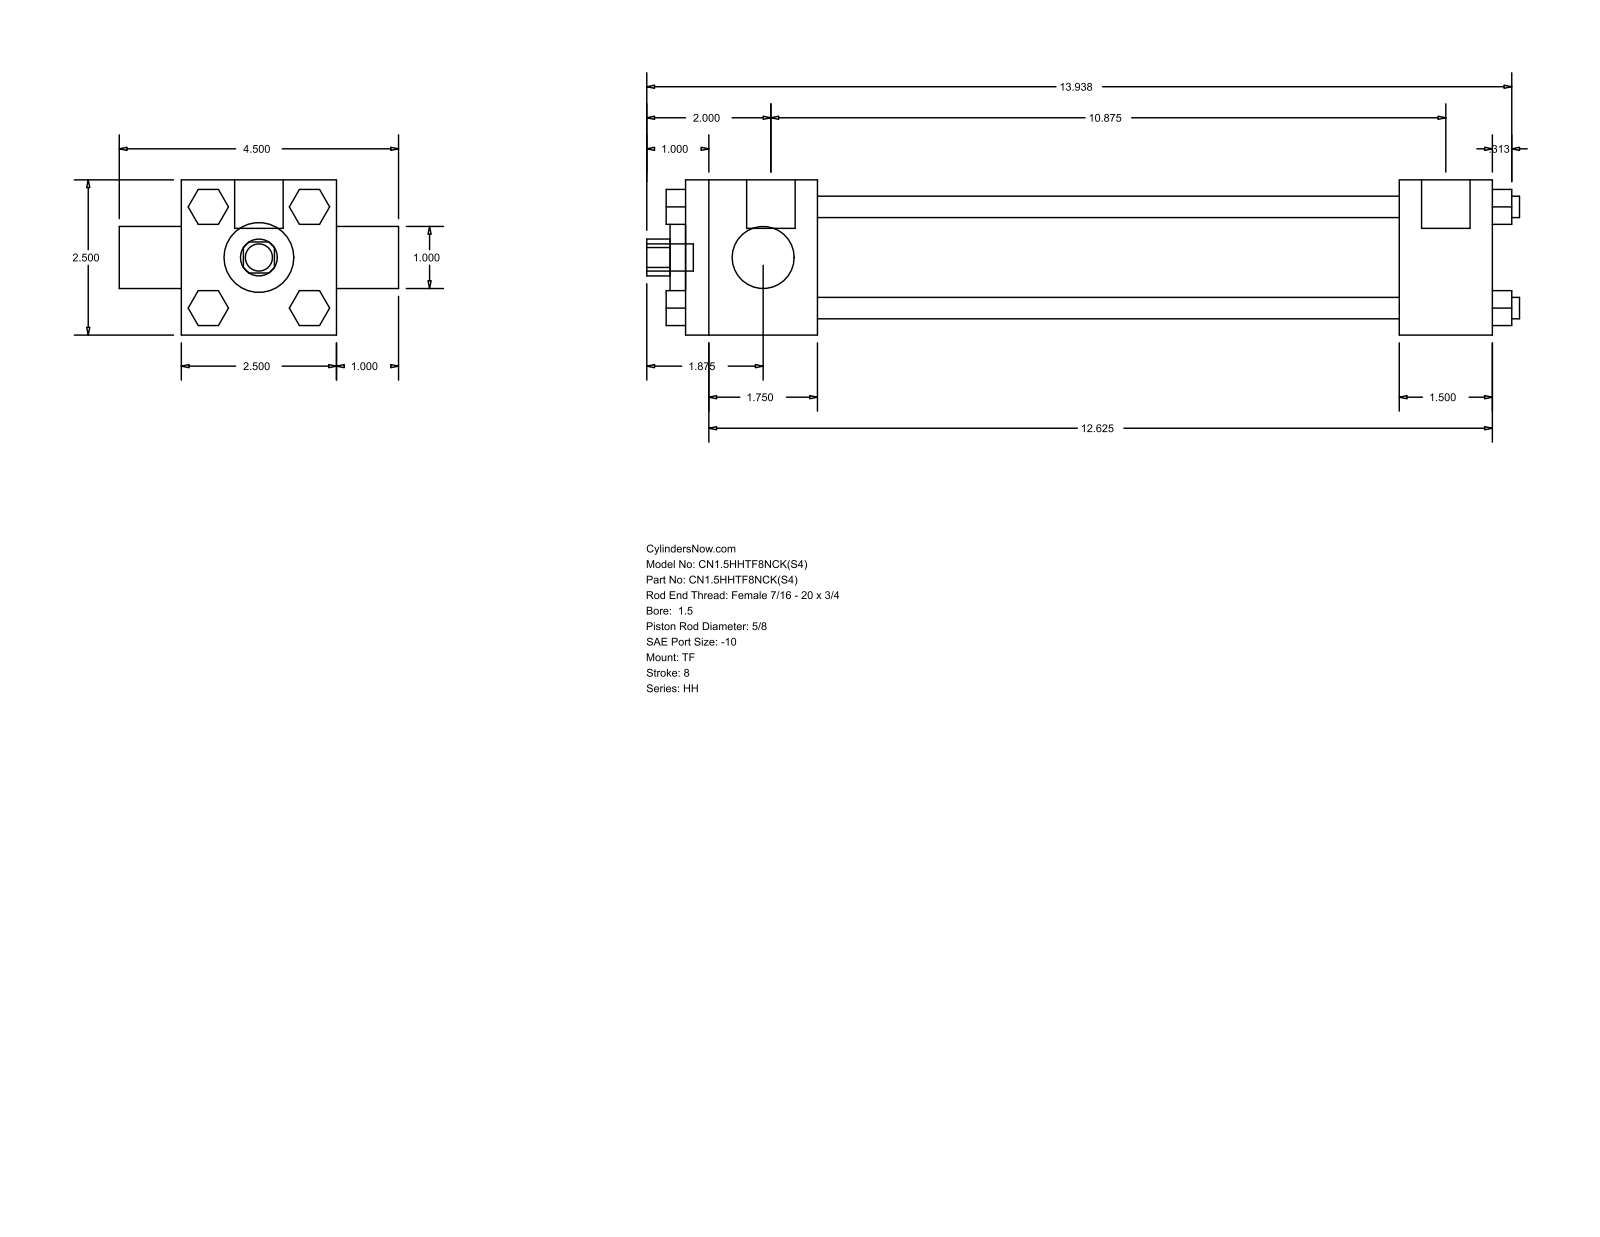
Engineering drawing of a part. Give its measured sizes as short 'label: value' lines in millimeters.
name: HH_TF__0150_0.625
written by: GSSL Pune (CONFIG_CONTROL_DESIGN)
unit: mm
bodies: 0 solids, 120 faces (92 planar, 28 cylindrical, 0 other)
size: 357.19 × 114.3 × 63.5
holes: 1× ⌀15.88, 1× ⌀25.4, 1× ⌀28.57, 1× ⌀44.45
bosses: 4× ⌀8.76, 3× ⌀5.56, 2× ⌀19.84, 1× ⌀11.11
rounds: 1× R7.54
face distances: 63.5, 330.19, 53.97, 276.22, 292.1, 238.13, 38.09, 25.4, 20.7, 14.29
